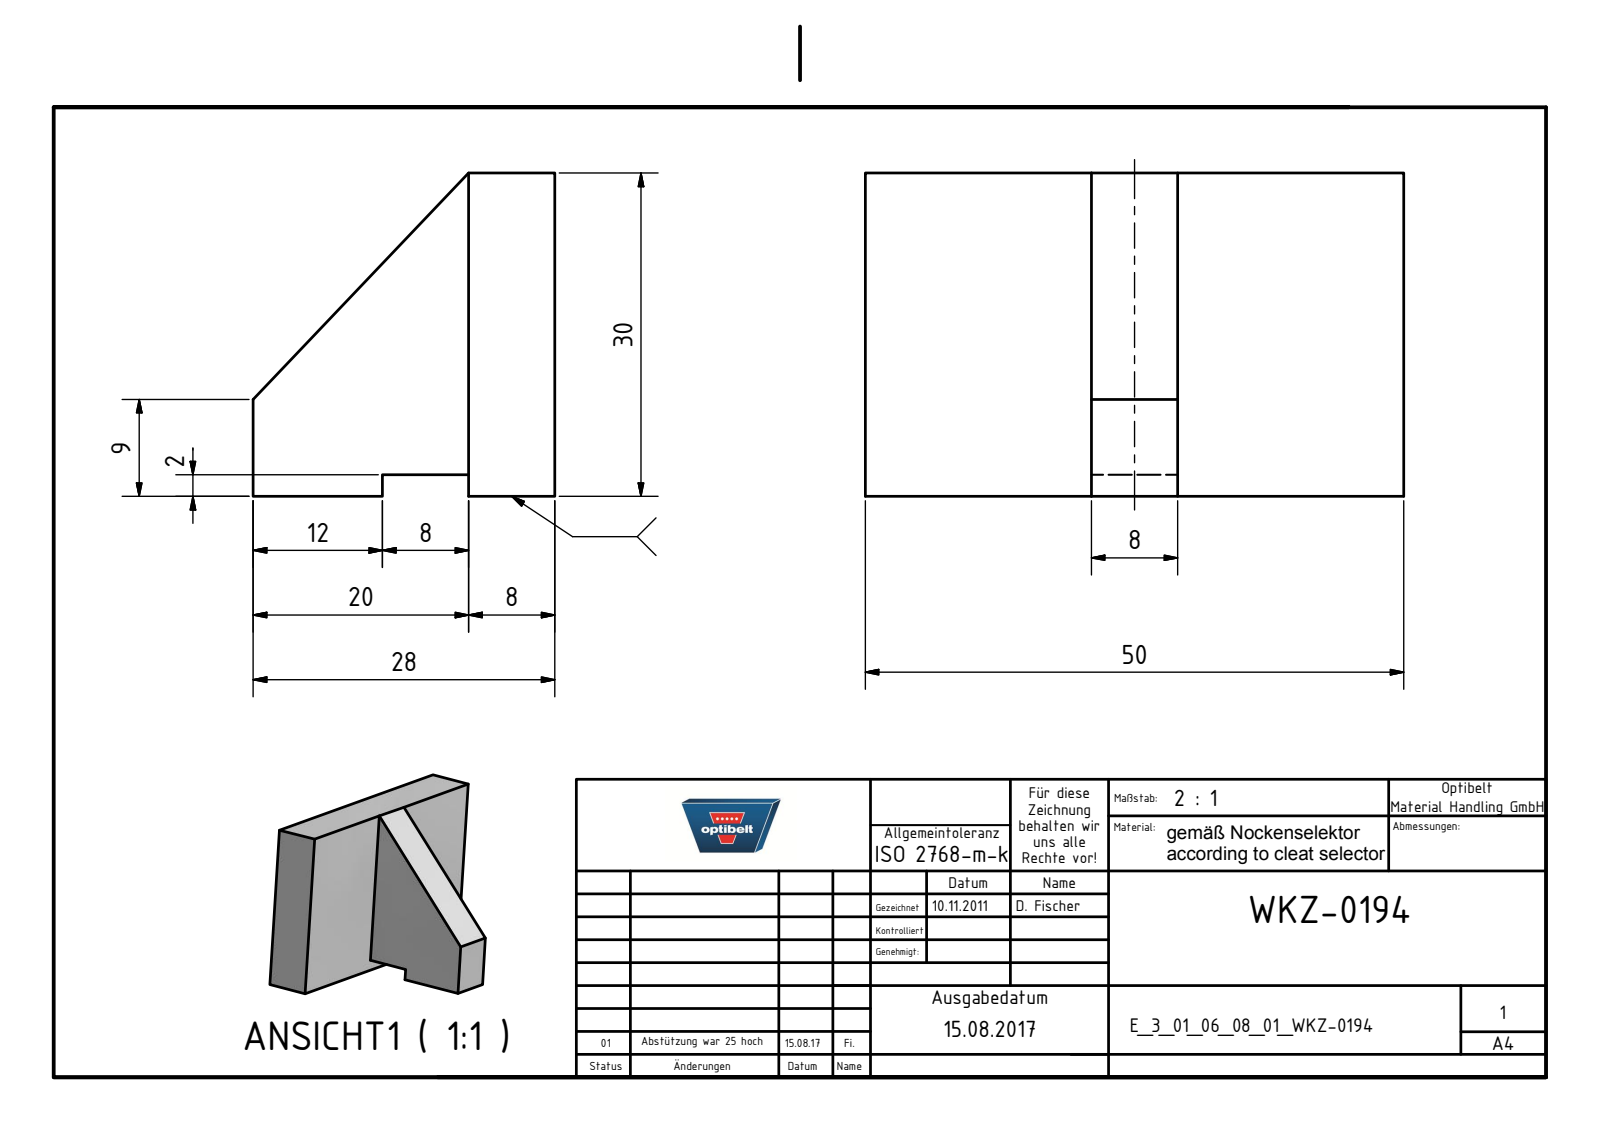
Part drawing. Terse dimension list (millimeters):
name: E_3_01_06_08_01_WKZ-0194
written by: Autodesk Inventor 2025 (AUTOMOTIVE_DESIGN)
unit: mm
bodies: 1 solid, 13 faces (13 planar, 0 cylindrical, 0 other)
size: 50 × 30 × 28
volume: 14 992 mm³; area: 5 284 mm²
face distances: 8, 21, 29, 30, 50, 28, 20, 2, 12, 16
